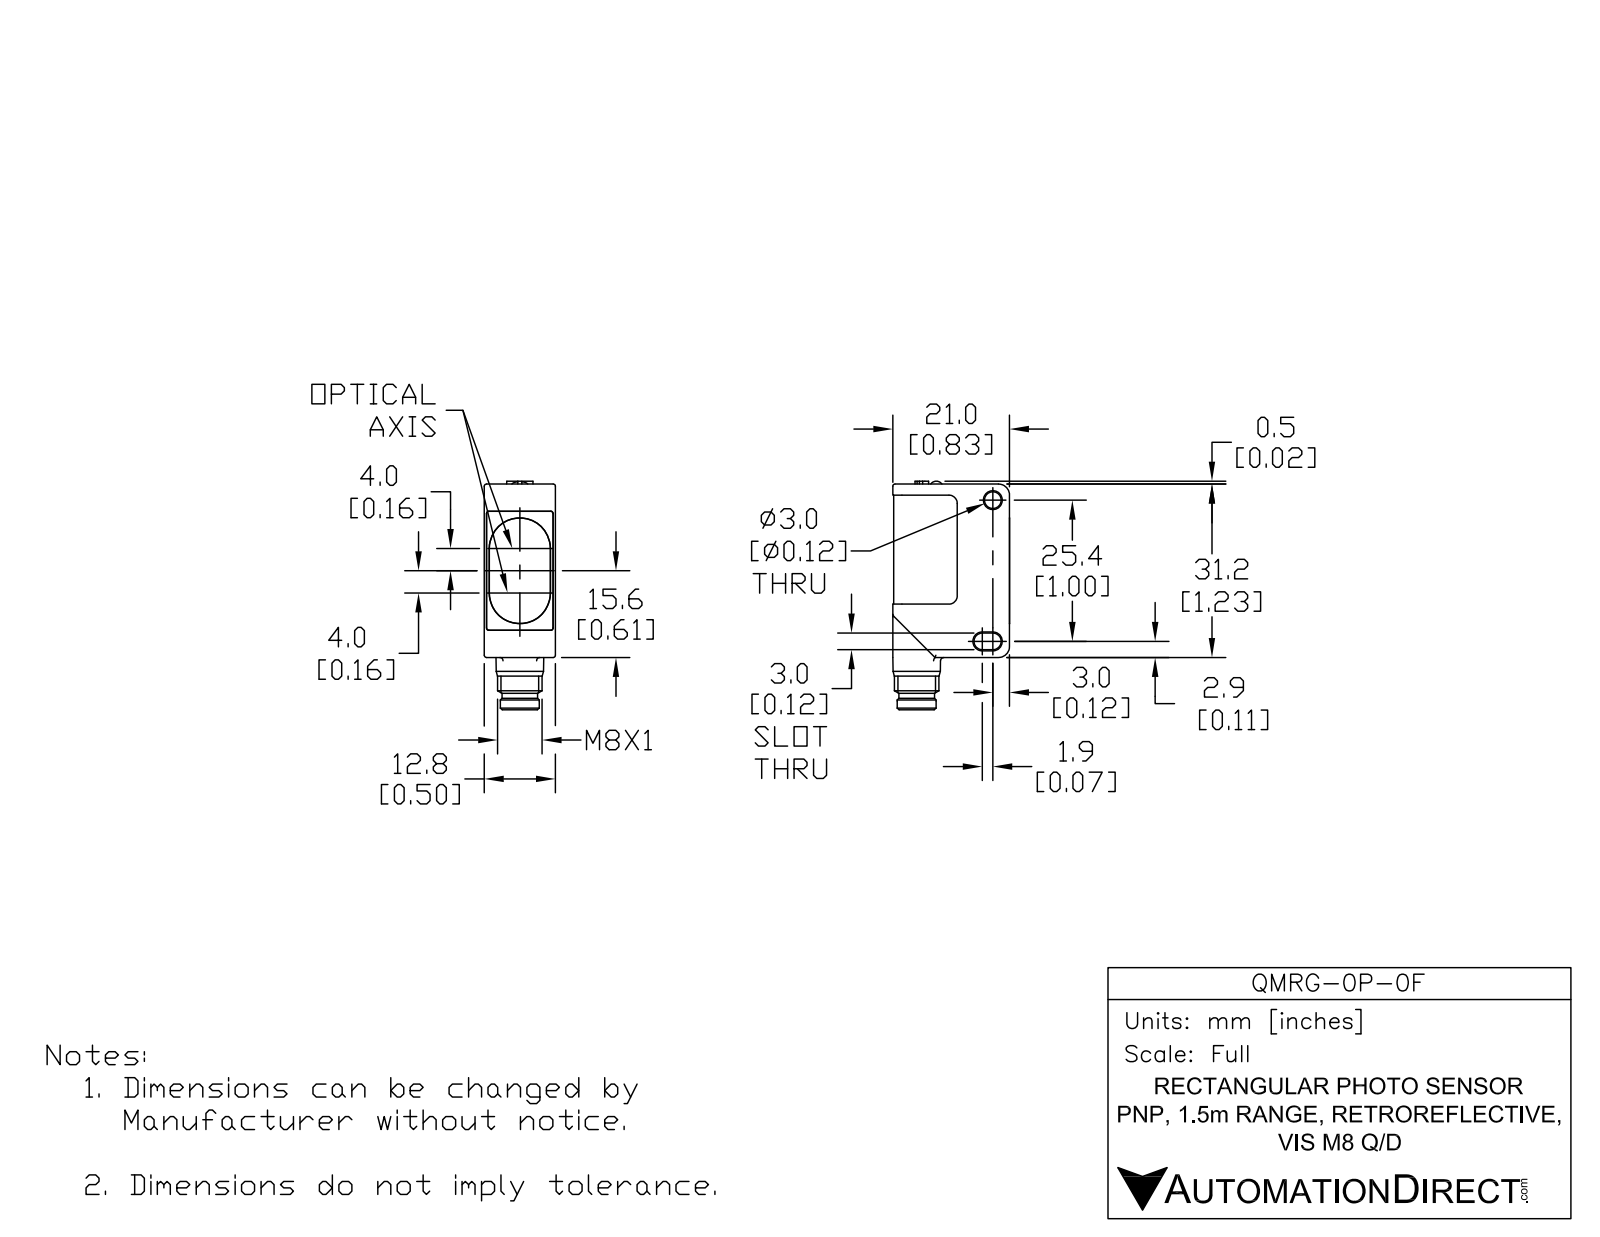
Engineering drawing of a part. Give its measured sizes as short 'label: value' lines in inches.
name: QMRG-0P-0F
written by: SolidWorks 2017 (AUTOMOTIVE_DESIGN)
unit: in
bodies: 7 solids, 272 faces (125 planar, 100 cylindrical, 47 other)
size: 1.619 × 0.827 × 0.504
volume: 0.474 in³; area: 7.749 in²
holes: 3× ⌀0.118, 1× ⌀0.228
bosses: 4× ⌀0.039, 2× ⌀0.138, 1× ⌀0.315, 1× ⌀0.276, 1× ⌀0.252
rounds: 10× R0.016, 9× R0.02, 6× R0.059, 4× R0.024, 4× R0.039, 2× R0.006, 2× R0.044, 2× R0.065
face distances: 0.498, 0.02, 0.504, 0.11, 0.016, 0.492, 0.488, 0.482, 0.059, 0.711
hole spacings: 0.04, 0.205, 0.245
